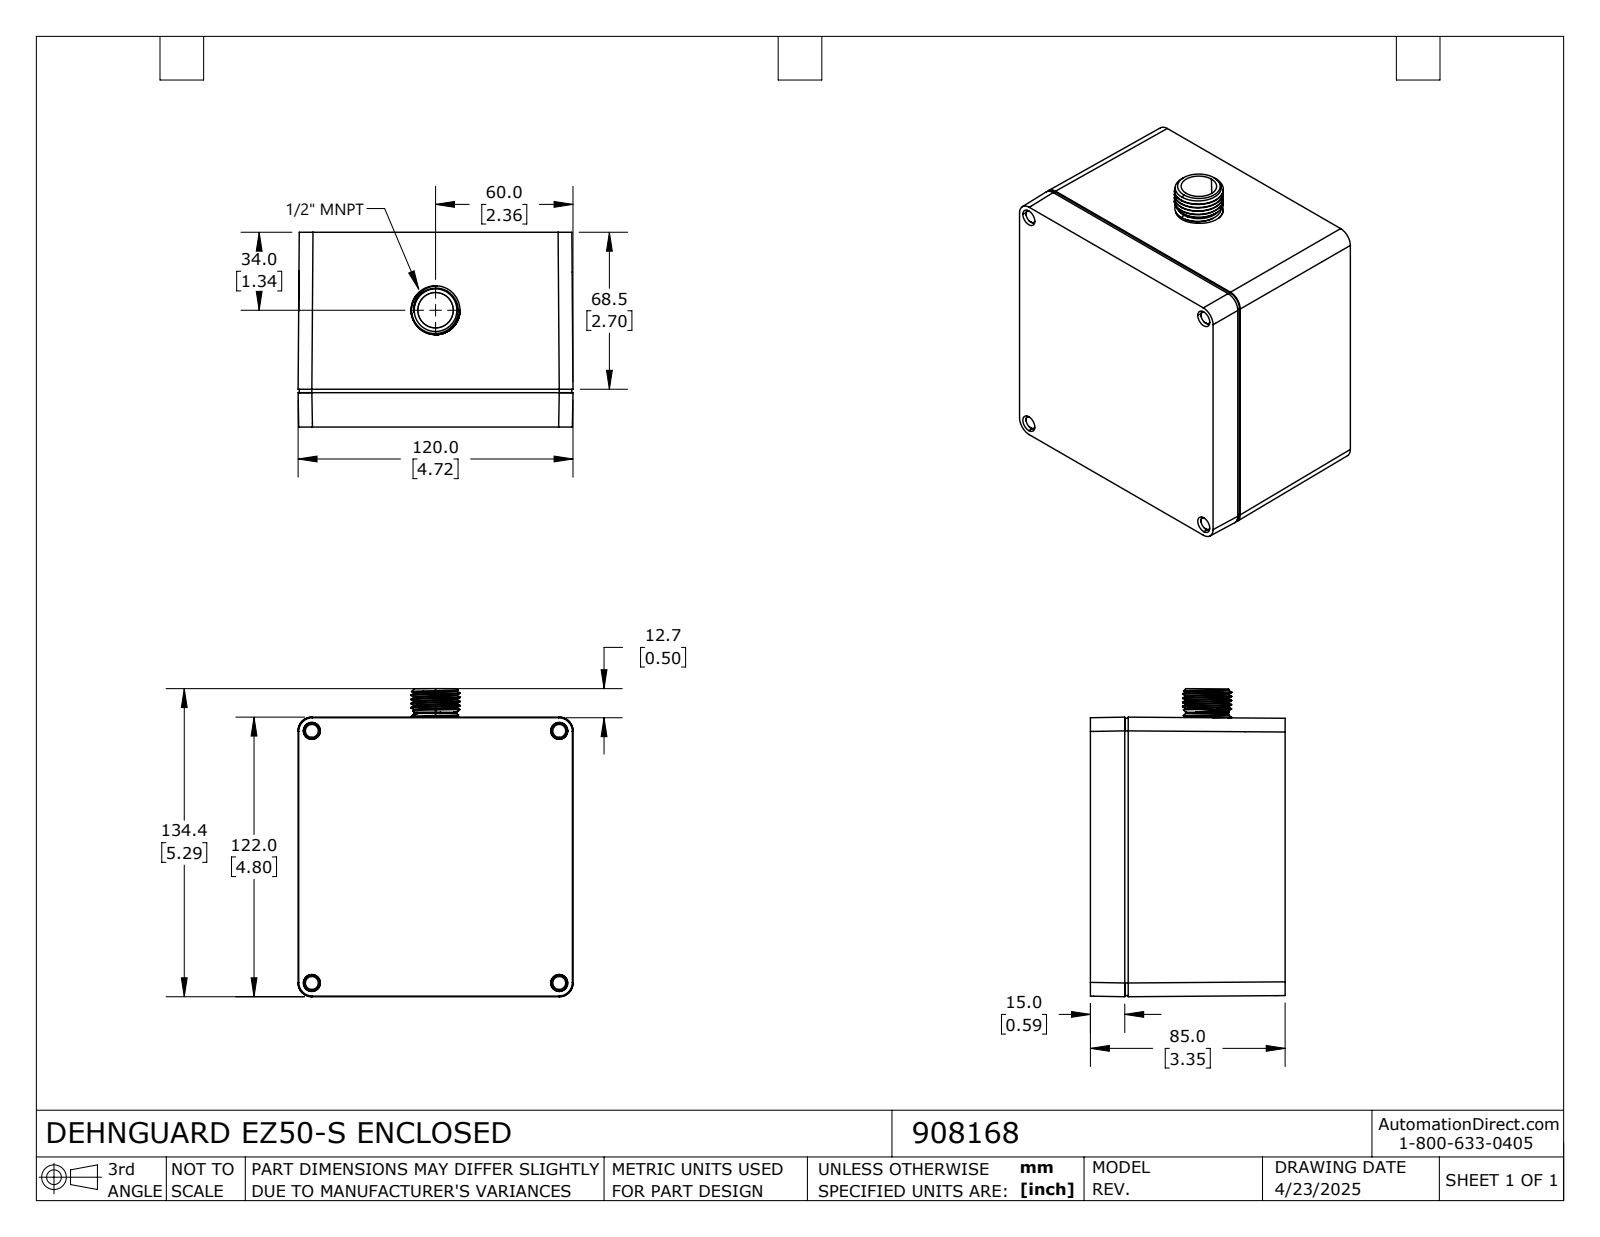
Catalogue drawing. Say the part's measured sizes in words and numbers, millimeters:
The part is named "908168". Its 3-D file was written by "SolidWorks 2024 (AUTOMOTIVE_DESIGN)". It is 2 solids with 610 faces: 378 planar, 162 cylindrical and 70 other. Overall it measures 134.4 by 120 by 85 millimeters. Its volume is 631 700 cubic millimeters and its surface area 192 100 square millimeters. Round holes: 4 of diameter 4.2, 4 of diameter 8. Round bosses or shafts: 6 of diameter 7, 4 of diameter 2.9, 1 of diameter 29.6, 1 of diameter 28.6, 1 of diameter 26.1, 1 of diameter 21.3. Partial cylindrical surfaces (rounded edges, fillets, slot ends): 8 of radius 0.1, 8 of radius 6, 4 of radius 5.5, 3 of radius 0.3, 3 of radius 0.5, 2 of radius 0.8, 2 of radius 2, 2 of radius 100. The main face-to-face distances are 3, 4, 85, 81, 82, 78, 3, 1, 9.4, 3. The hole center spacings are 90, 110, 142.1.
